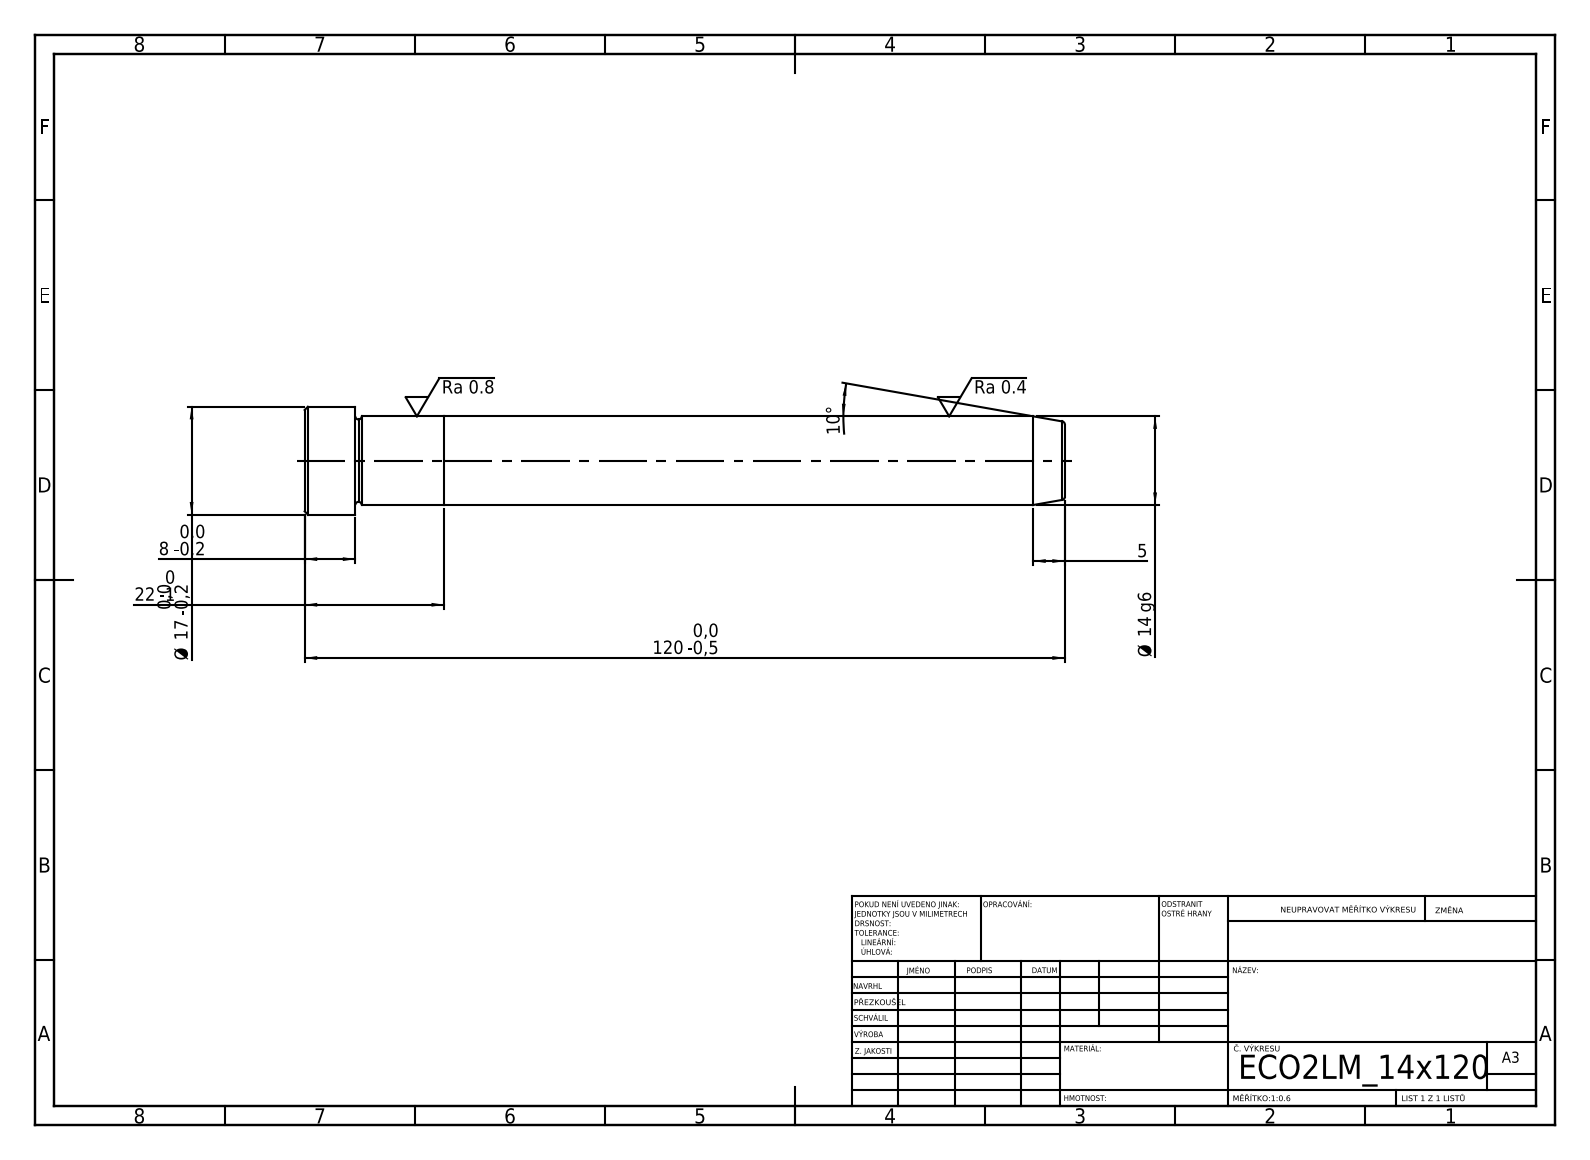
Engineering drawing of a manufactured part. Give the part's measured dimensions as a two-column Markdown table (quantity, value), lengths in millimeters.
| quantity | value |
| --- | --- |
| STEP written by | SolidWorks 2019 (CONFIG_CONTROL_DESIGN) |
| units | millimeters |
| bodies | 2 solids, 21 faces (5 planar, 6 cylindrical, 10 other) |
| overall size | 120 × 17 × 17 |
| volume | 18 939 mm³ |
| surface area | 6 069 mm² |
| round bosses / shafts (diameter × count) | 17 × 1, 14 × 1 |
| main face-to-face distances | 22, 98, 120, 112, 14, 8 |
